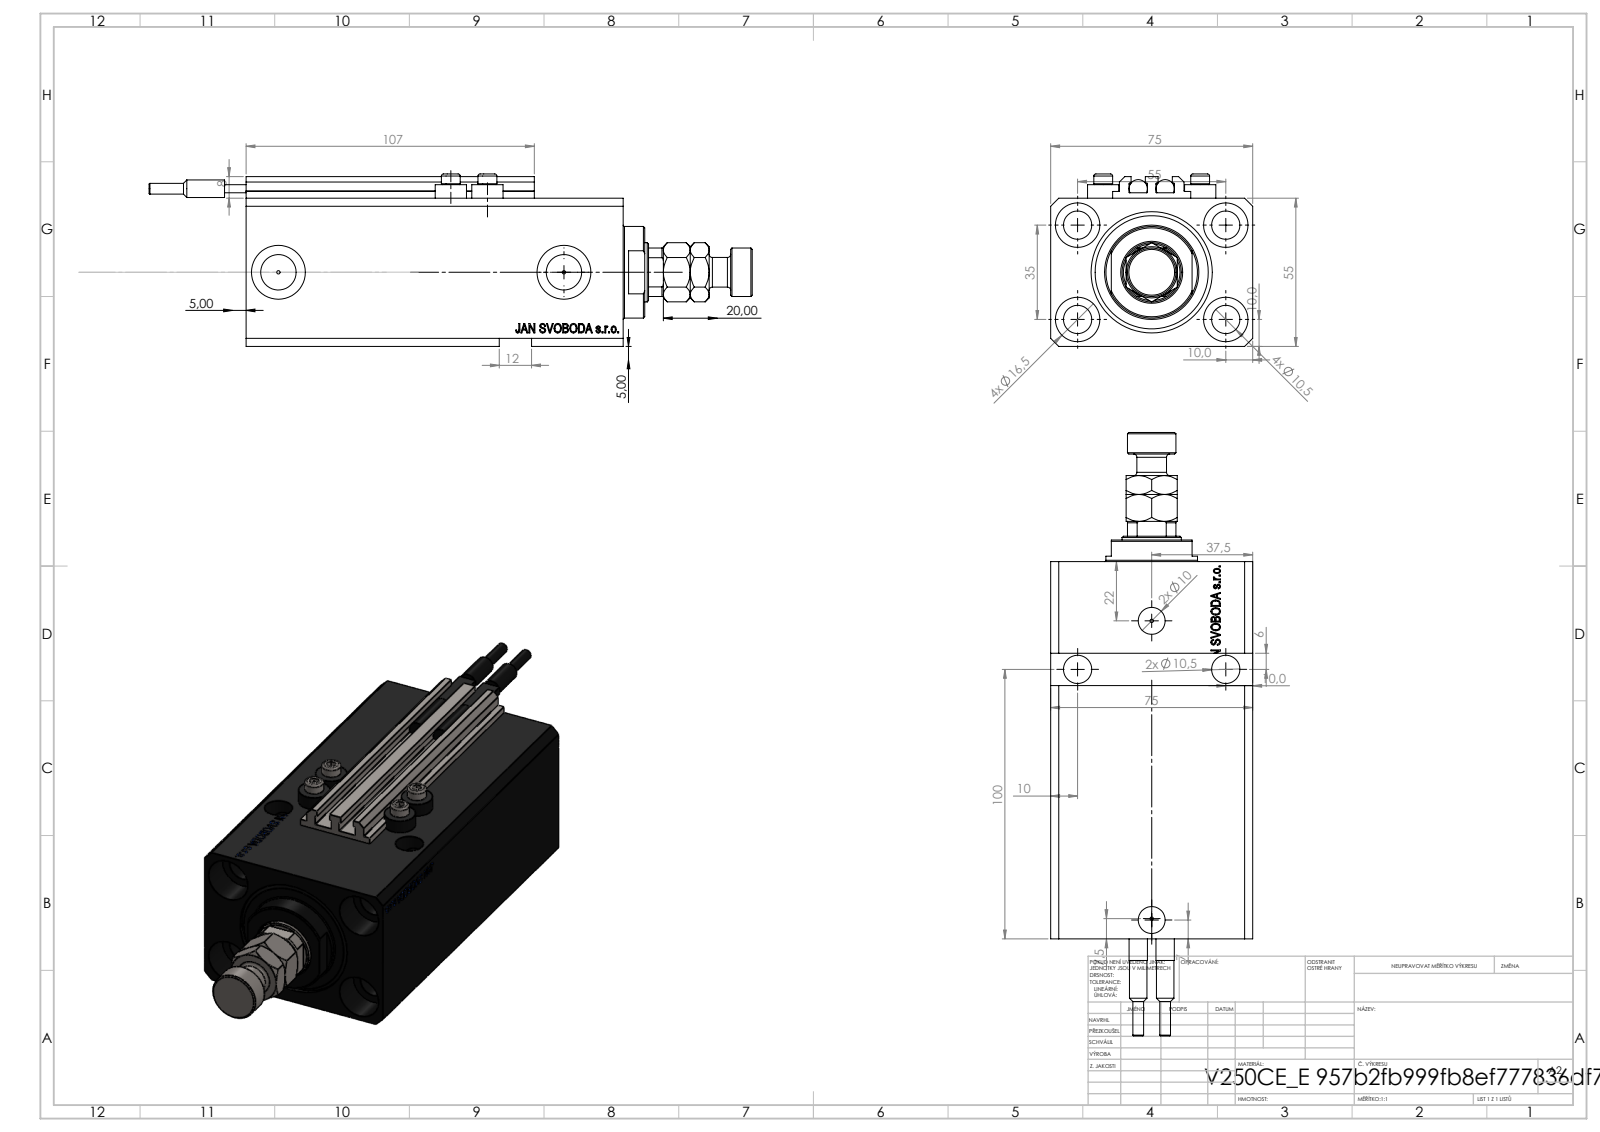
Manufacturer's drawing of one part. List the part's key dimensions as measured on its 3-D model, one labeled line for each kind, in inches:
Part name (STEP PRODUCT): SWITCH_V250CE; V250CE_E_Body; ALLEN BOLT V250CE; V250CE_C_VCP (+2 more)
STEP written by: SolidWorks 2019 (CONFIG_CONTROL_DESIGN)
Units: inches
Bodies: 11 solids, 1188 faces (562 planar, 162 cylindrical, 464 other)
Overall size (bounding box): 8.819 × 2.953 × 2.52
Volume: 30.32 in³ · Surface area: 187.2 in²
Round holes (diameter × count): ⌀0.413 ×9, ⌀0.049 ×4, ⌀0.157 ×4, ⌀0.65 ×4, ⌀0.394 ×2, ⌀0.518 ×2, ⌀0.787 ×2, ⌀0.866 ×1, ⌀1.26 ×1, ⌀1.772 ×1
Round bosses / shafts (diameter × count): ⌀0.457 ×4, ⌀0.276 ×4, ⌀0.268 ×2, ⌀0.256 ×2, ⌀0.157 ×2, ⌀1.339 ×1, ⌀0.709 ×1, ⌀0.433 ×1
Partial cylindrical surfaces — rounded edges, fillets, slot ends (radius × count): R0.008 ×10, R0.413 ×1
Main face-to-face distances: 2.165, 2.953, 0.591, 0.118, 2.244, 5.512, 4.921, 0.098, 0.39, 0.079
Hole centre spacings: 1.283, 1.294, 2.165, 3.818, 0.535, 0.555, 1.016, 1.283
